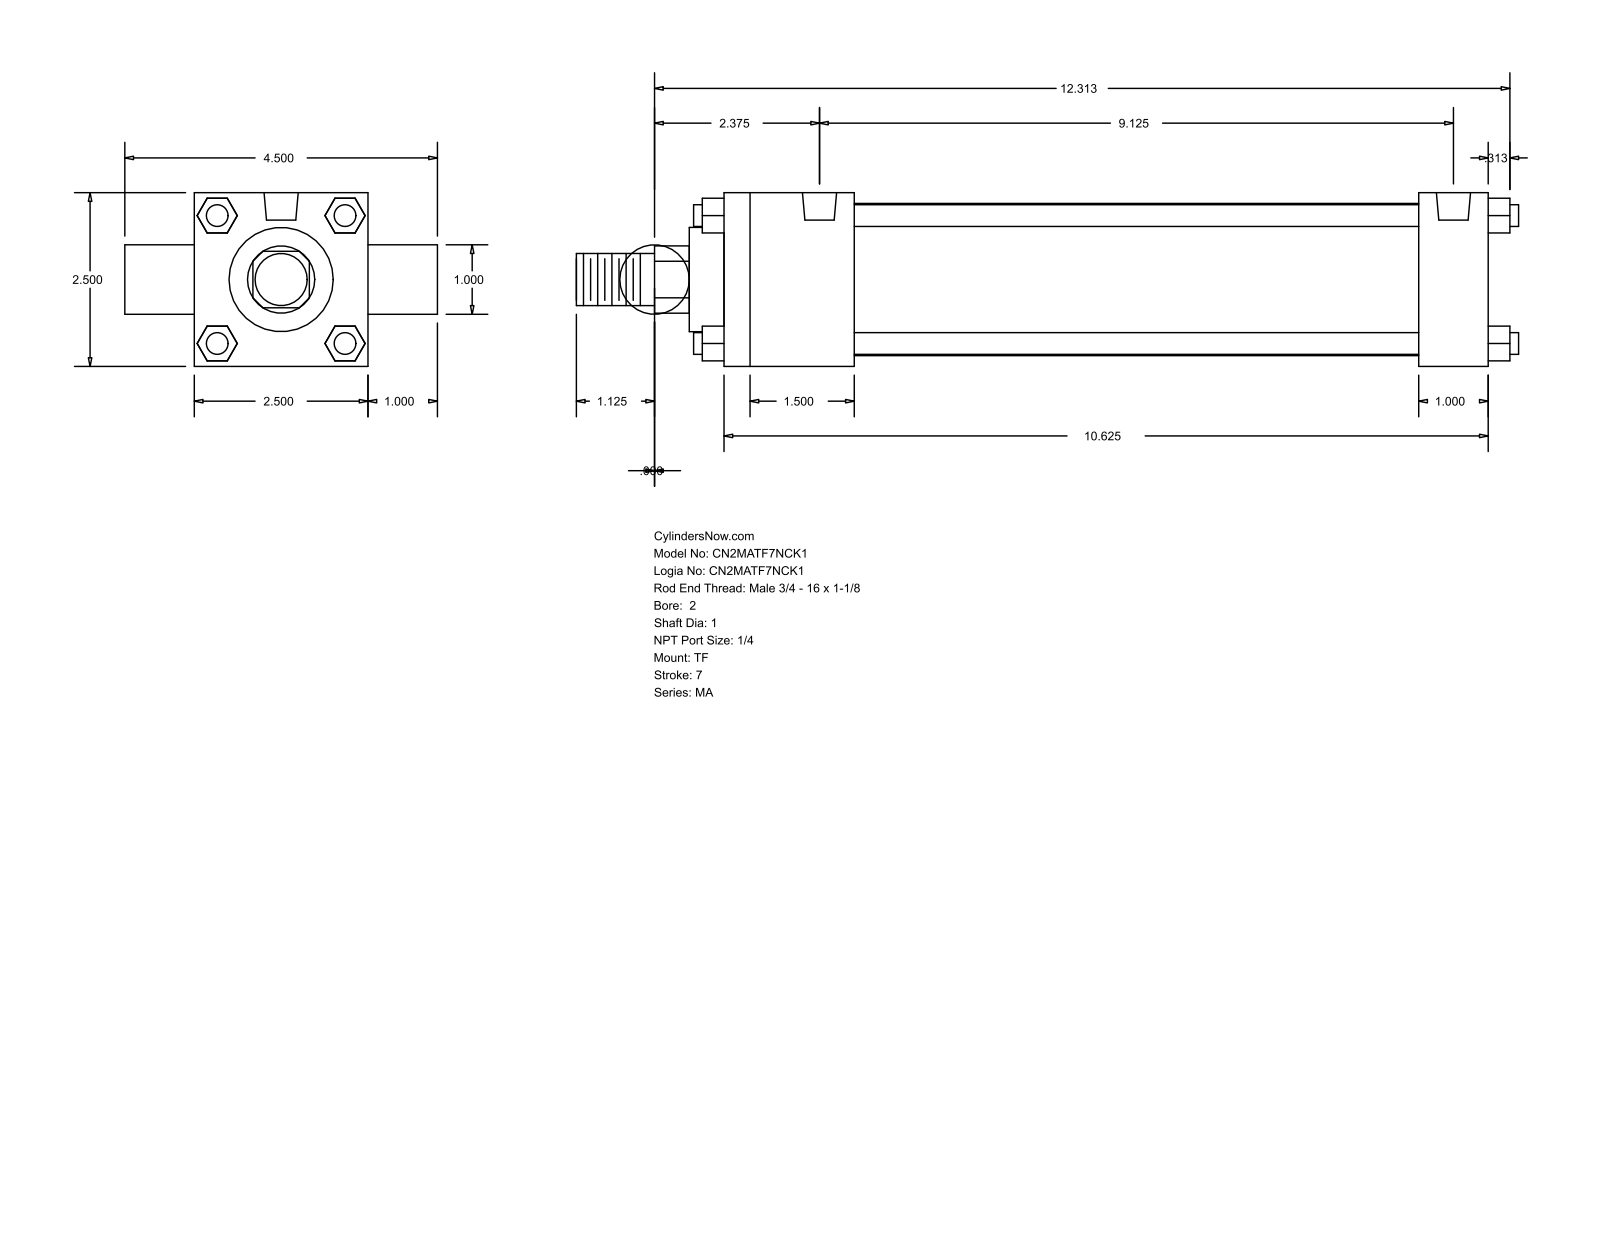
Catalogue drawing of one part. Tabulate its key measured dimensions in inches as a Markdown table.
| quantity | value |
| --- | --- |
| part name | MA_TF__0200_1 |
| STEP written by | GSSL Pune (CONFIG_CONTROL_DESIGN) |
| units | inches |
| bodies | 0 solids, 120 faces (92 planar, 28 cylindrical, 0 other) |
| overall size | 13.563 × 4.5 × 2.5 |
| round holes (diameter × count) | 0.313 × 3, 0.492 × 2 |
| round bosses / shafts (diameter × count) | 0.313 × 4, 1 × 2, 2.19 × 1, 1.5 × 1, 0.75 × 1 |
| partial cylindrical surfaces (radius × count) | 0.484 × 1 |
| main face-to-face distances | 2.5, 1, 11, 0.5, 1.875, 10, 8.125, 9.125, 3.5, 0.92 |
| hole center spacings | 9.125 |
